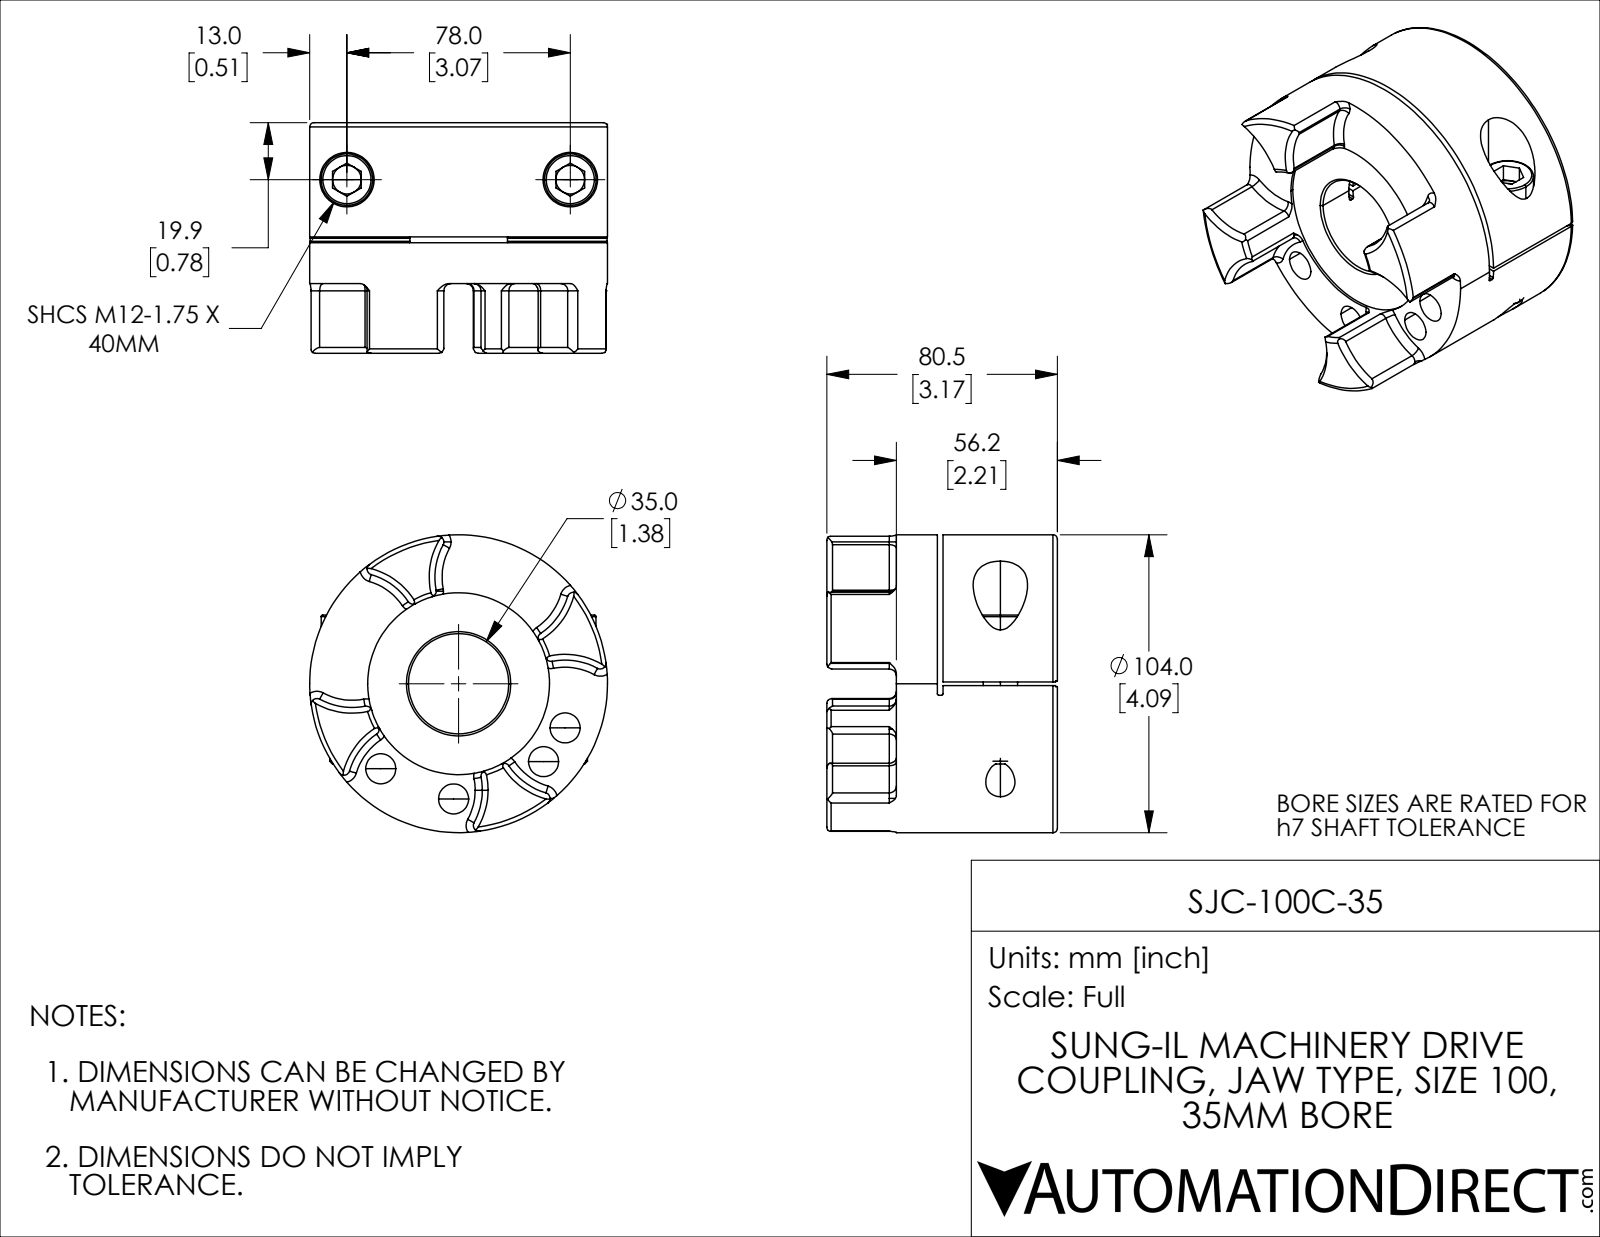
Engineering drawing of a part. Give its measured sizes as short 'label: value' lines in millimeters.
name: SJC-100C-35
written by: SolidWorks 2021 (CONFIG_CONTROL_DESIGN)
unit: mm
bodies: 4 solids, 222 faces (55 planar, 82 cylindrical, 85 other)
size: 104 × 104 × 80.5
volume: 429 579 mm³; area: 72 243 mm²
holes: 4× ⌀10.5, 2× ⌀10, 2× ⌀10.2, 2× ⌀12.5, 2× ⌀19, 1× ⌀35, 1× ⌀63.5
bosses: 2× ⌀18, 2× ⌀12, 1× ⌀104
rounds: 16× R2, 4× R23.68, 2× R0.5, 1× R75
face distances: 2, 41.9, 39.9, 56.2, 16.3, 14.3, 55.3, 15.4, 13.4, 0.9
hole spacings: 40.25, 13.98, 27.52, 34.03, 46.18, 56.92, 65.94, 78
